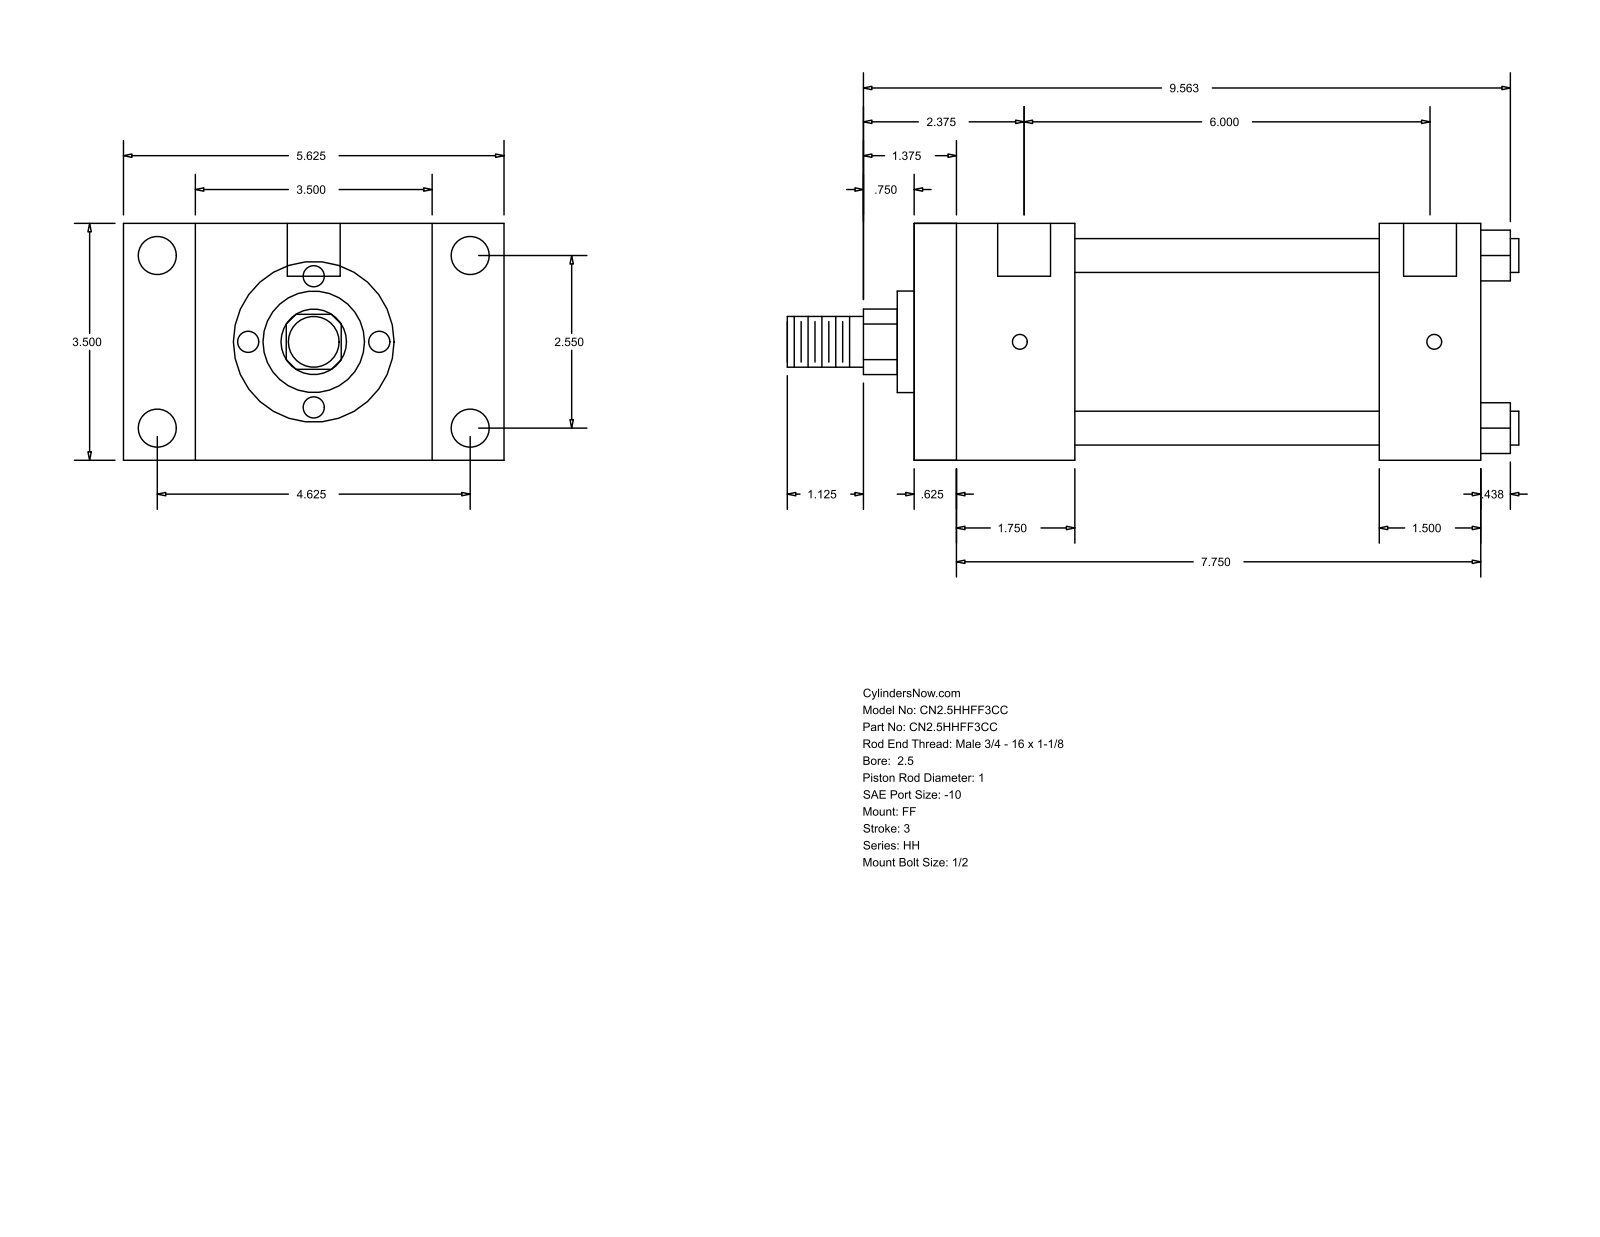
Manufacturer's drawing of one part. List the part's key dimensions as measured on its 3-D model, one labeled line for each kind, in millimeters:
Part name (STEP PRODUCT): HH_FF__0250_1
STEP written by: GSSL Pune (CONFIG_CONTROL_DESIGN)
Units: millimetres
Bodies: 0 solids, 92 faces (64 planar, 28 cylindrical, 0 other)
Overall size (bounding box): 274.64 × 142.88 × 88.9
Round holes (diameter × count): ⌀5.56 ×4, ⌀14.3 ×4, ⌀19.84 ×2
Round bosses / shafts (diameter × count): ⌀12.7 ×4, ⌀73.03 ×1, ⌀38.1 ×1, ⌀25.4 ×1, ⌀19.05 ×1
Partial cylindrical surfaces — rounded edges, fillets, slot ends (radius × count): R12.29 ×1
Main face-to-face distances: 88.9, 212.73, 15.87, 196.86, 38.1, 60.33, 44.46, 152.4, 174.63, 158.76
Hole centre spacings: 1.59, 64.76, 117.48, 134.15, 153.98, 155.57, 152.39
